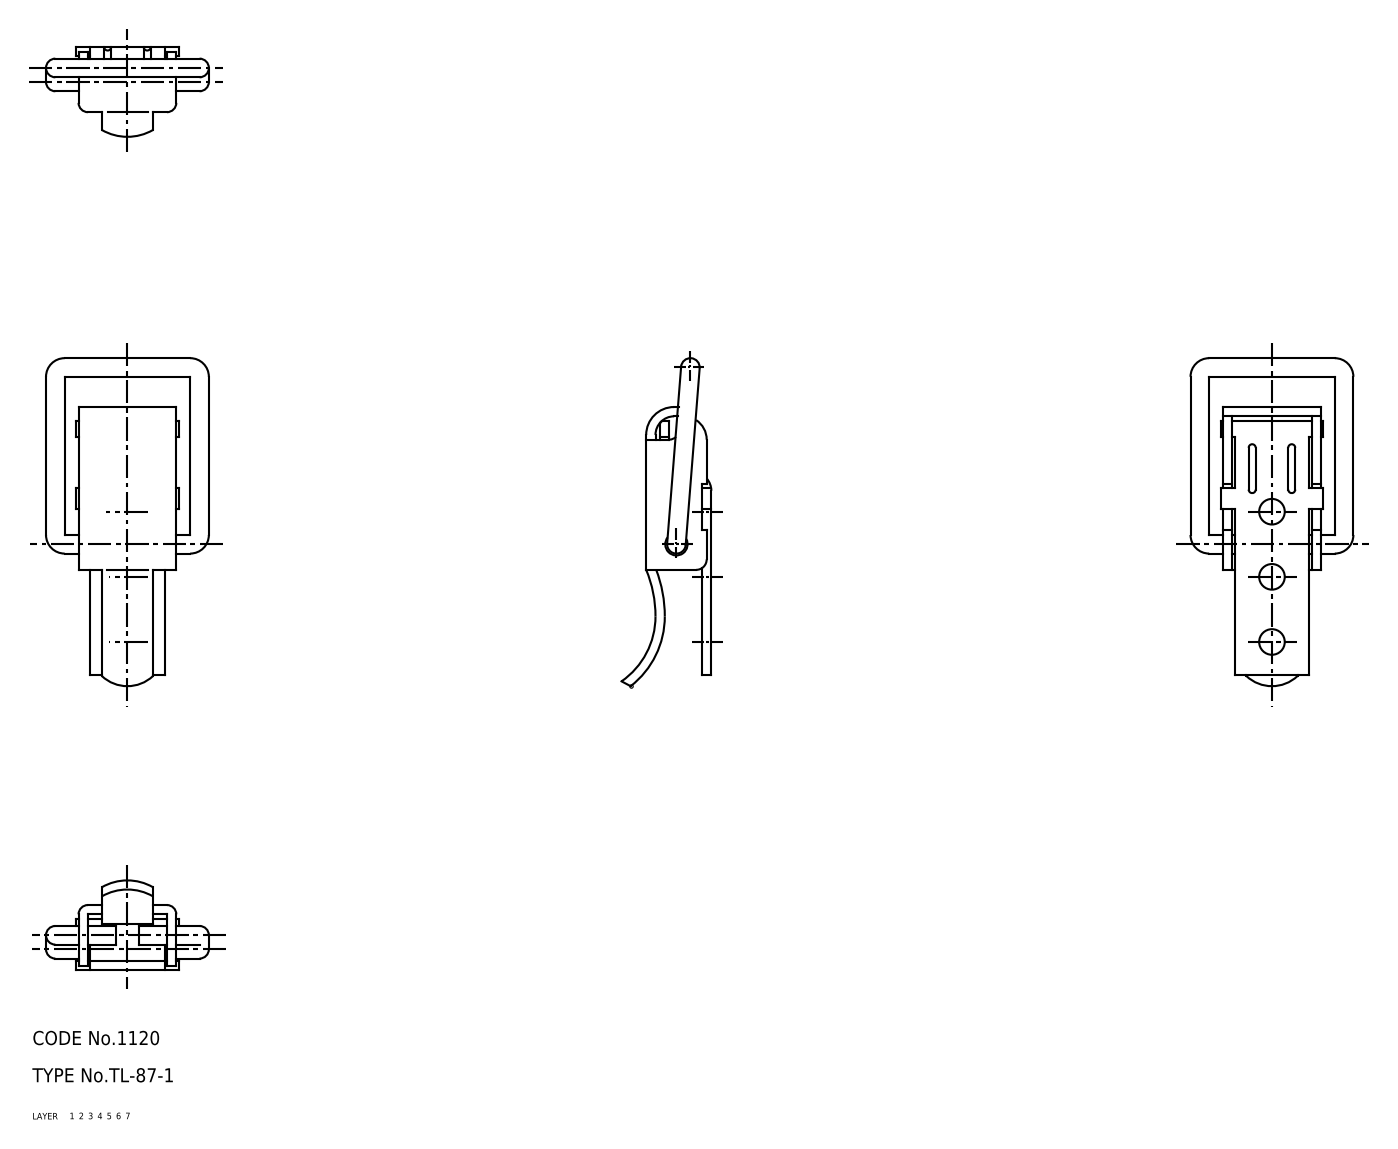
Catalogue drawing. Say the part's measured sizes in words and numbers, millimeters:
The part is named "lever; base; arm; TL_87_1_21297_36". Its 3-D file was written by "CADfix (AUTOMOTIVE_DESIGN)". It is 3 solids with 155 faces: 0 planar, 0 cylindrical and 155 other. Overall it measures 70.5 by 35 by 19.3 millimeters. Its volume is 6 851 cubic millimeters and its surface area 7 864 square millimeters.
